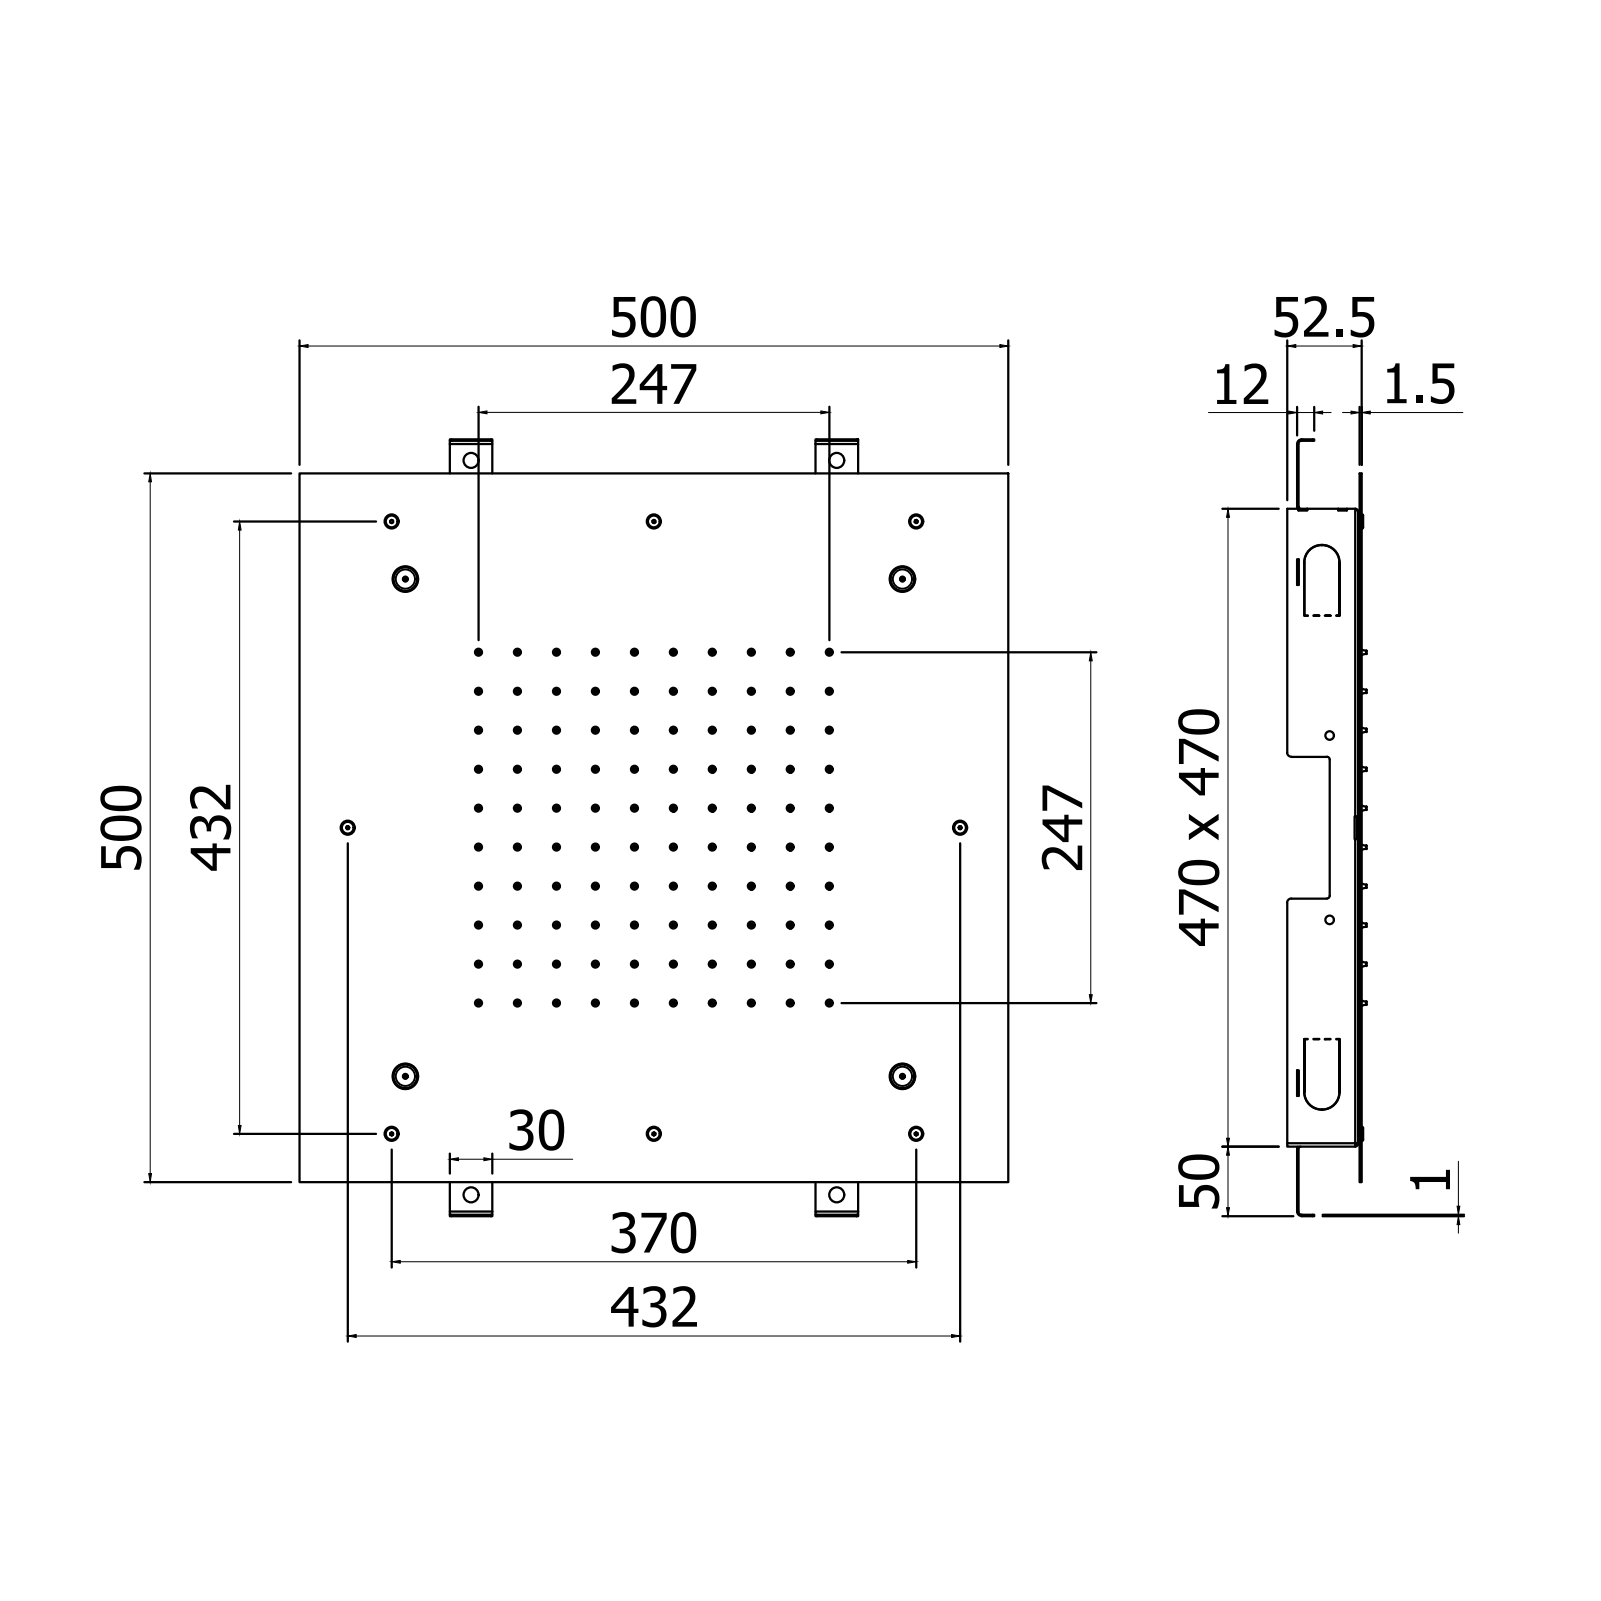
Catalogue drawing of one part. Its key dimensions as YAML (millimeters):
part_name: "ZSOF129CR"
step_written_by: "CREO PARAMETRIC BY PTC INC, 2020044 (CONFIG_CONTROL_DESIGN)"
units: millimeters
bodies: {solids: 1, faces: 1786, planar: 182, cylindrical: 532, other: 1072}
overall_size: [500, 500, 4.8]
volume: 376972
surface_area: 512310
round_holes:
  - {diameter: 1.5, count: 104}
  - {diameter: 5, count: 100}
  - {diameter: 7, count: 8}
  - {diameter: 17.05, count: 4}
round_bosses_or_shafts:
  - {diameter: 10, count: 8}
  - {diameter: 5, count: 8}
  - {diameter: 20, count: 4}
  - {diameter: 16.65, count: 4}
partial_cylinders:
  - {radius: 0.2, count: 48}
  - {radius: 2, count: 4}
face_to_face_distances: [1.5, 500, 2.5, 1, 4.8, 3.3, 2.3, 2, 208, 104]
hole_center_spacings: [61.49, 137.5, 86.96, 38.89, 99.15, 167.28, 122.98, 140.22]
